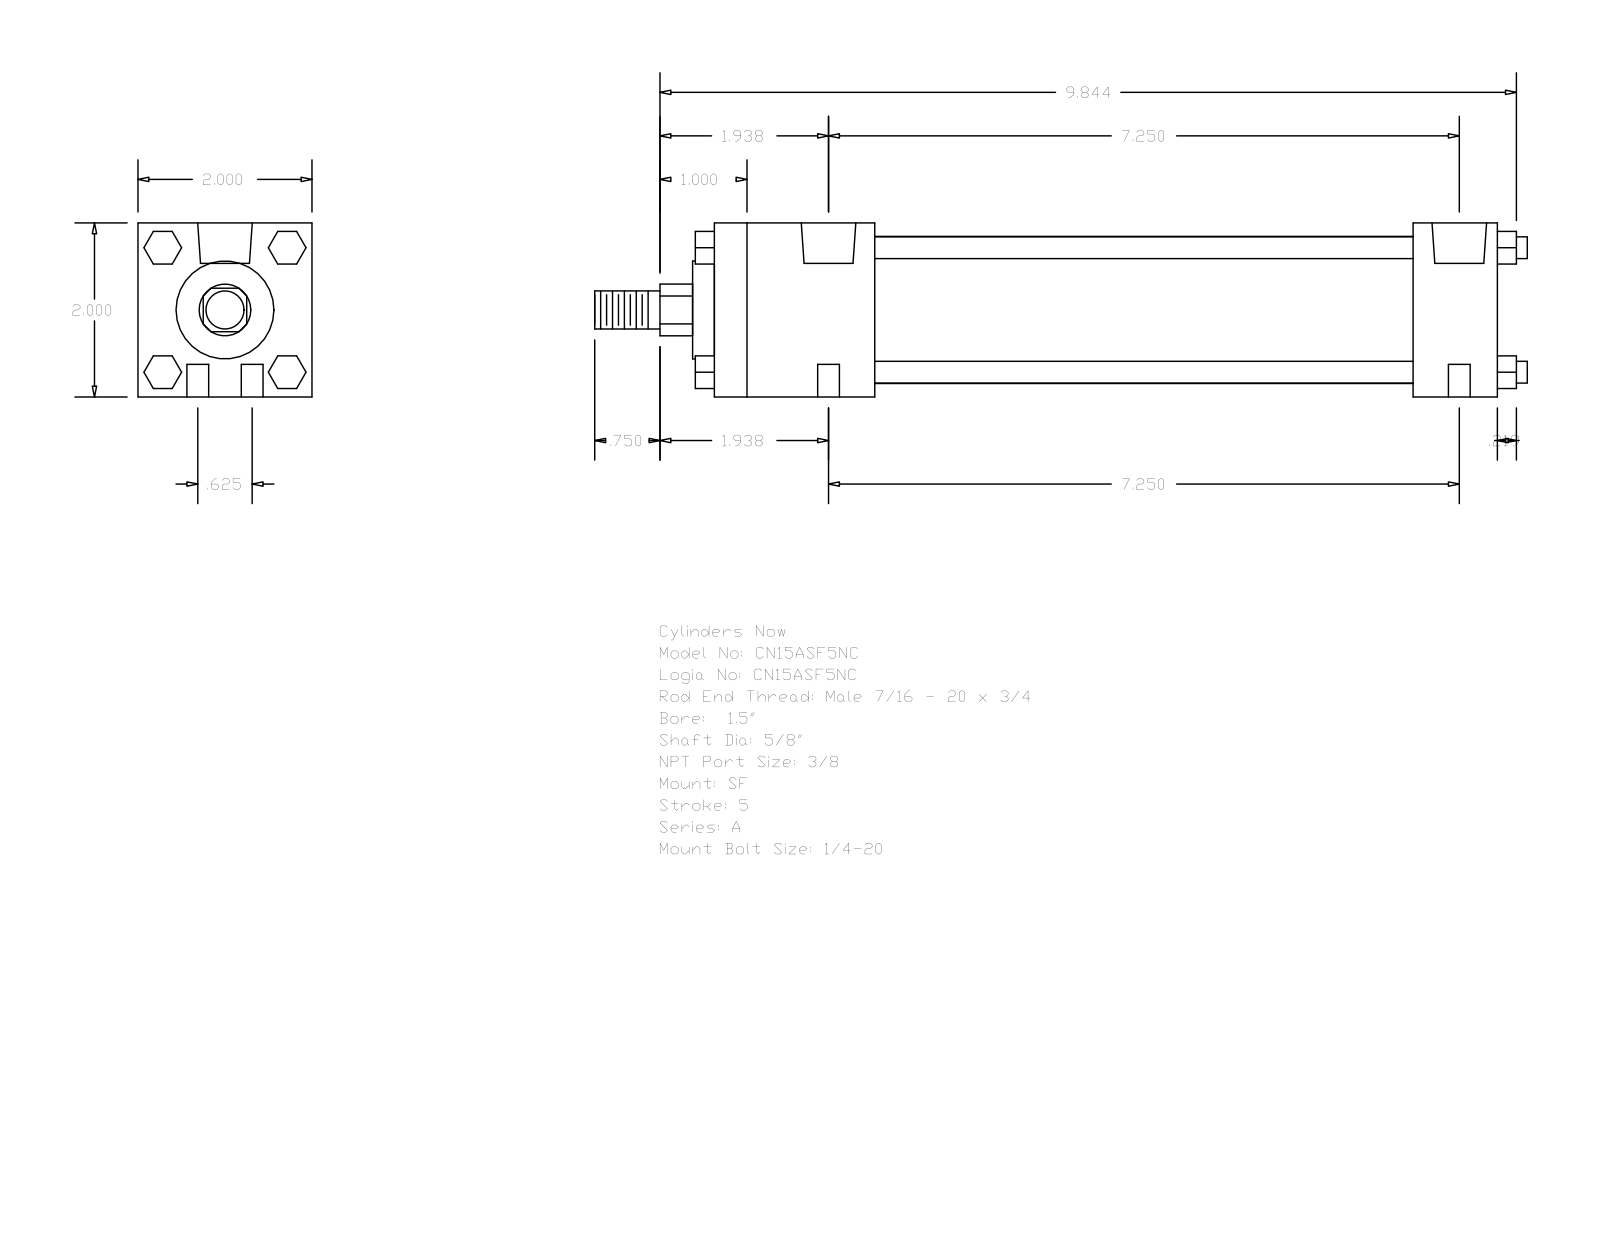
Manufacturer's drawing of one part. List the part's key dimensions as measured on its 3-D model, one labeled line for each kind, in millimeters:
Part name (STEP PRODUCT): A_SF__0150_0.625
STEP written by: GSSL Pune (CONFIG_CONTROL_DESIGN)
Units: millimetres
Bodies: 0 solids, 124 faces (94 planar, 30 cylindrical, 0 other)
Overall size (bounding box): 272.26 × 50.8 × 50.8
Round holes (diameter × count): ⌀6.35 ×4, ⌀5.56 ×2, ⌀15.93 ×2
Round bosses / shafts (diameter × count): ⌀6.35 ×4, ⌀42.93 ×1, ⌀28.57 ×1, ⌀15.88 ×1, ⌀11.11 ×1
Partial cylindrical surfaces — rounded edges, fillets, slot ends (radius × count): R7.54 ×1
Main face-to-face distances: 50.8, 228.59, 46.83, 203.99, 157.16, 181.76, 24.6, 6.35, 9.52, 53.18
Hole centre spacings: 7.94, 184.32, 184.15, 15.88, 184.83, 176.21
